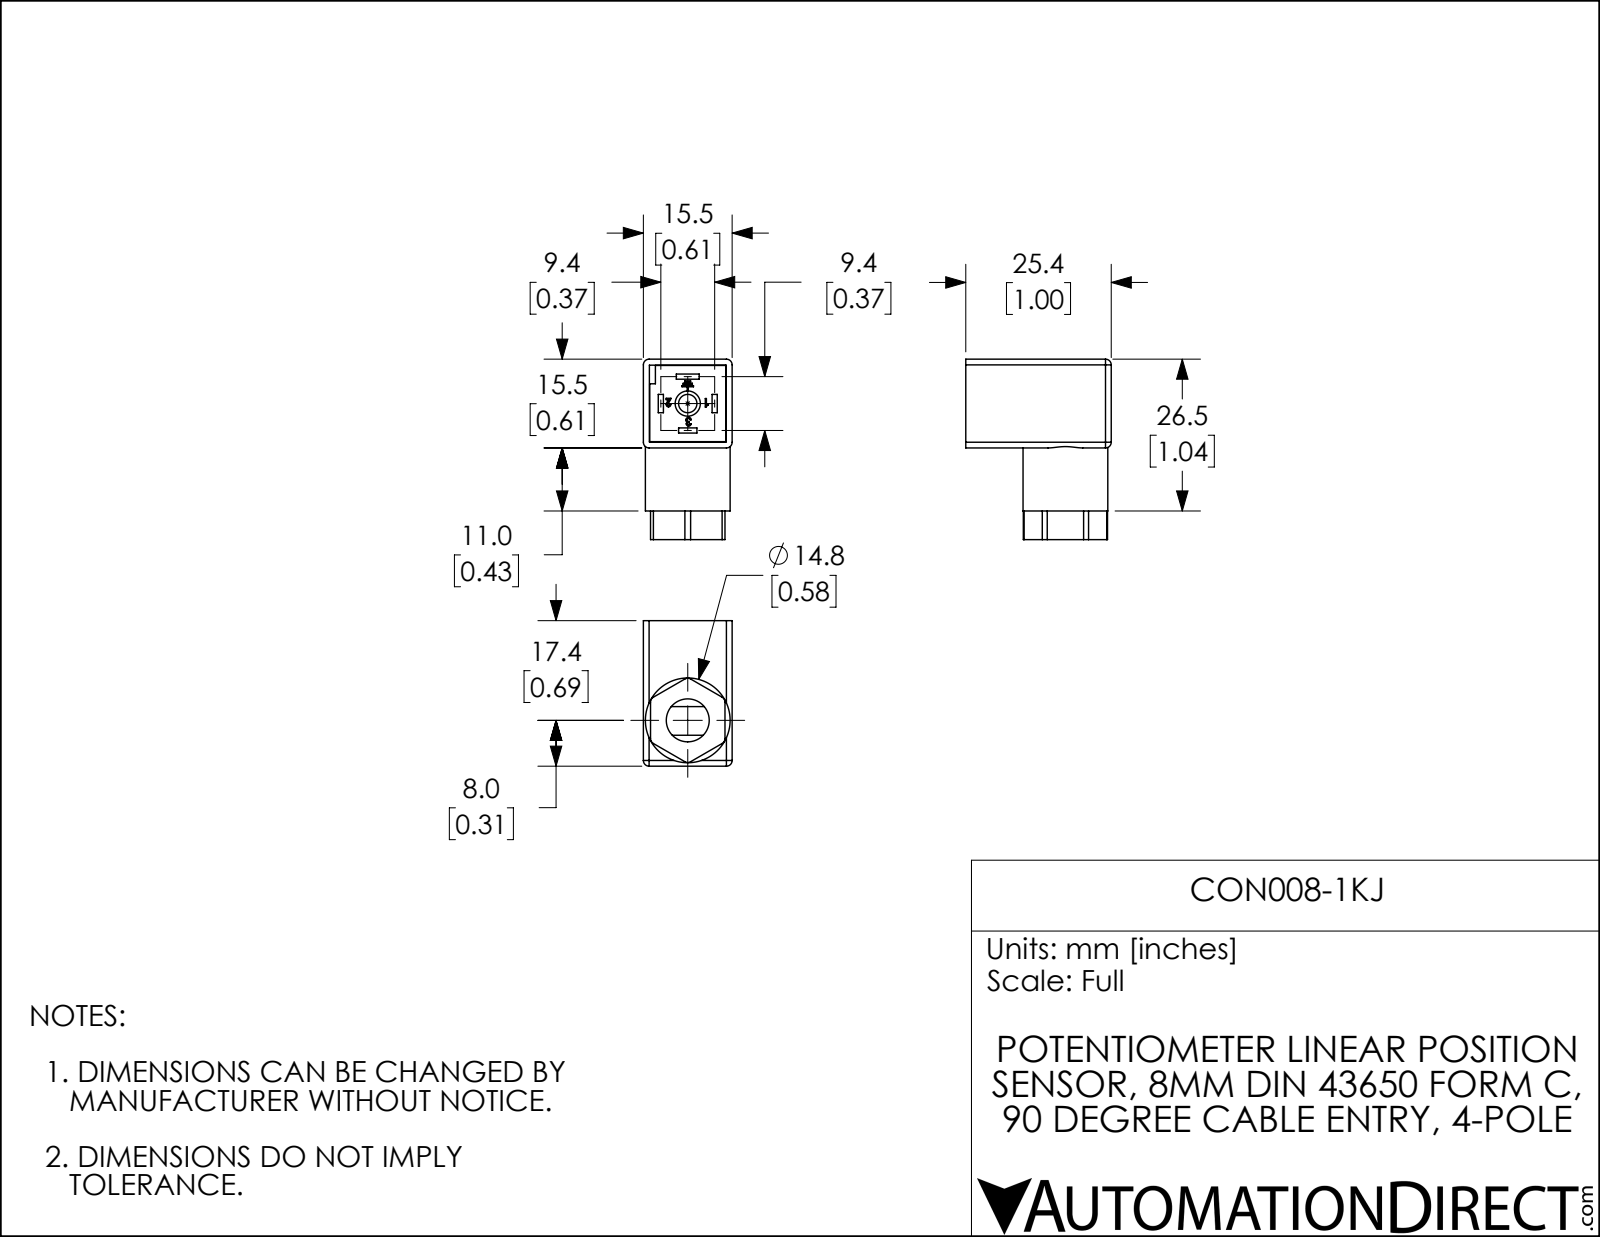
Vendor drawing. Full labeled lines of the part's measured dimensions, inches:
Part name (STEP PRODUCT): CON008-1KJ
STEP written by: SolidWorks 2019 (AUTOMOTIVE_DESIGN)
Units: inches
Bodies: 2 solids, 133 faces (85 planar, 19 cylindrical, 29 other)
Overall size (bounding box): 1.24 × 1 × 0.61
Volume: 0.392 in³ · Surface area: 8.977 in²
Round holes (diameter × count): ⌀0.126 ×1, ⌀0.173 ×1, ⌀0.295 ×1, ⌀0.307 ×1
Round bosses / shafts (diameter × count): ⌀0.583 ×1
Partial cylindrical surfaces — rounded edges, fillets, slot ends (radius × count): R0.039 ×14
Main face-to-face distances: 0.041, 0.569, 0.526, 0.567, 0.043, 0.528, 0.61, 0.524, 0.591, 0.197
